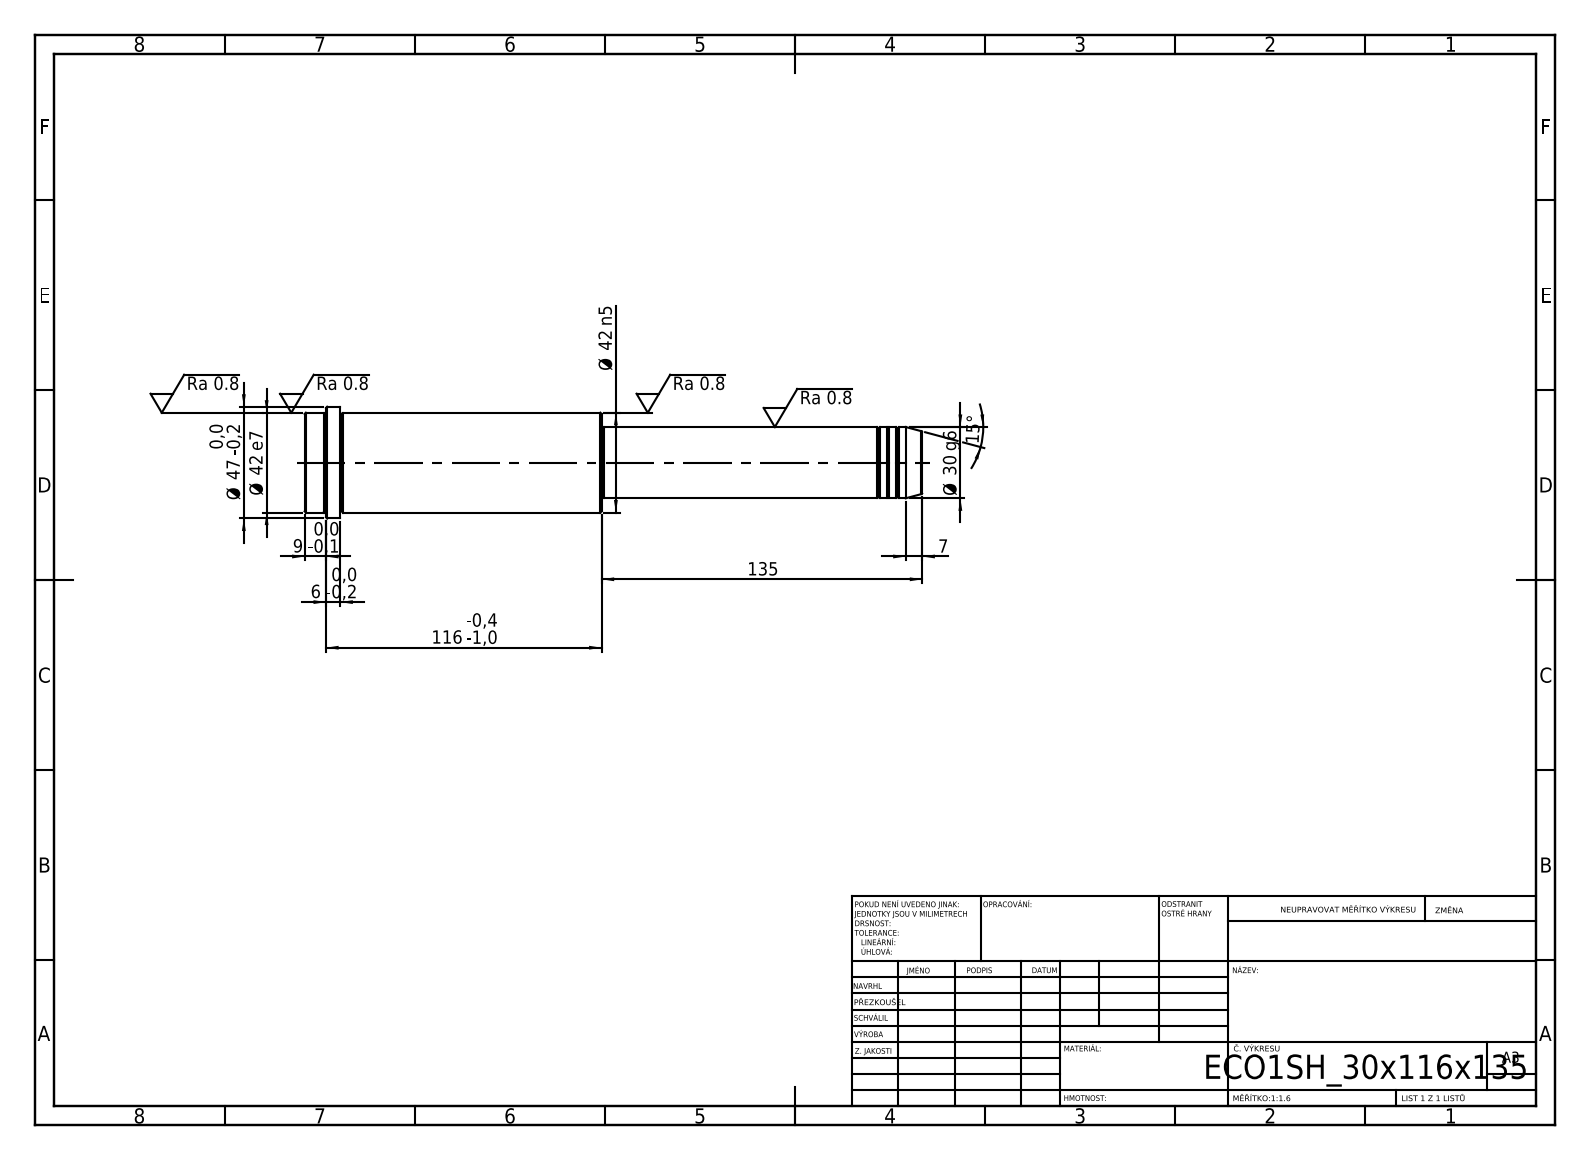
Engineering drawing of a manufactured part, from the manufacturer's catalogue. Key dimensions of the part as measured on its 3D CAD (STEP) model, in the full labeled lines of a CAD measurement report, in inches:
STEP written by: SolidWorks 2019 (CONFIG_CONTROL_DESIGN)
Units: inches
Bodies: 1 solid, 52 faces (6 planar, 16 cylindrical, 30 other)
Overall size (bounding box): 10.236 × 1.85 × 1.85
Volume: 16.46 in³ · Surface area: 50.92 in²
Round bosses / shafts (diameter × count): ⌀1.85 ×1, ⌀1.654 ×1, ⌀1.181 ×1, ⌀1.142 ×1
Main face-to-face distances: 4.921, 5.315, 10.236, 9.646, 4.331, 0.591, 9.882, 4.567, 0.236, 0.354
